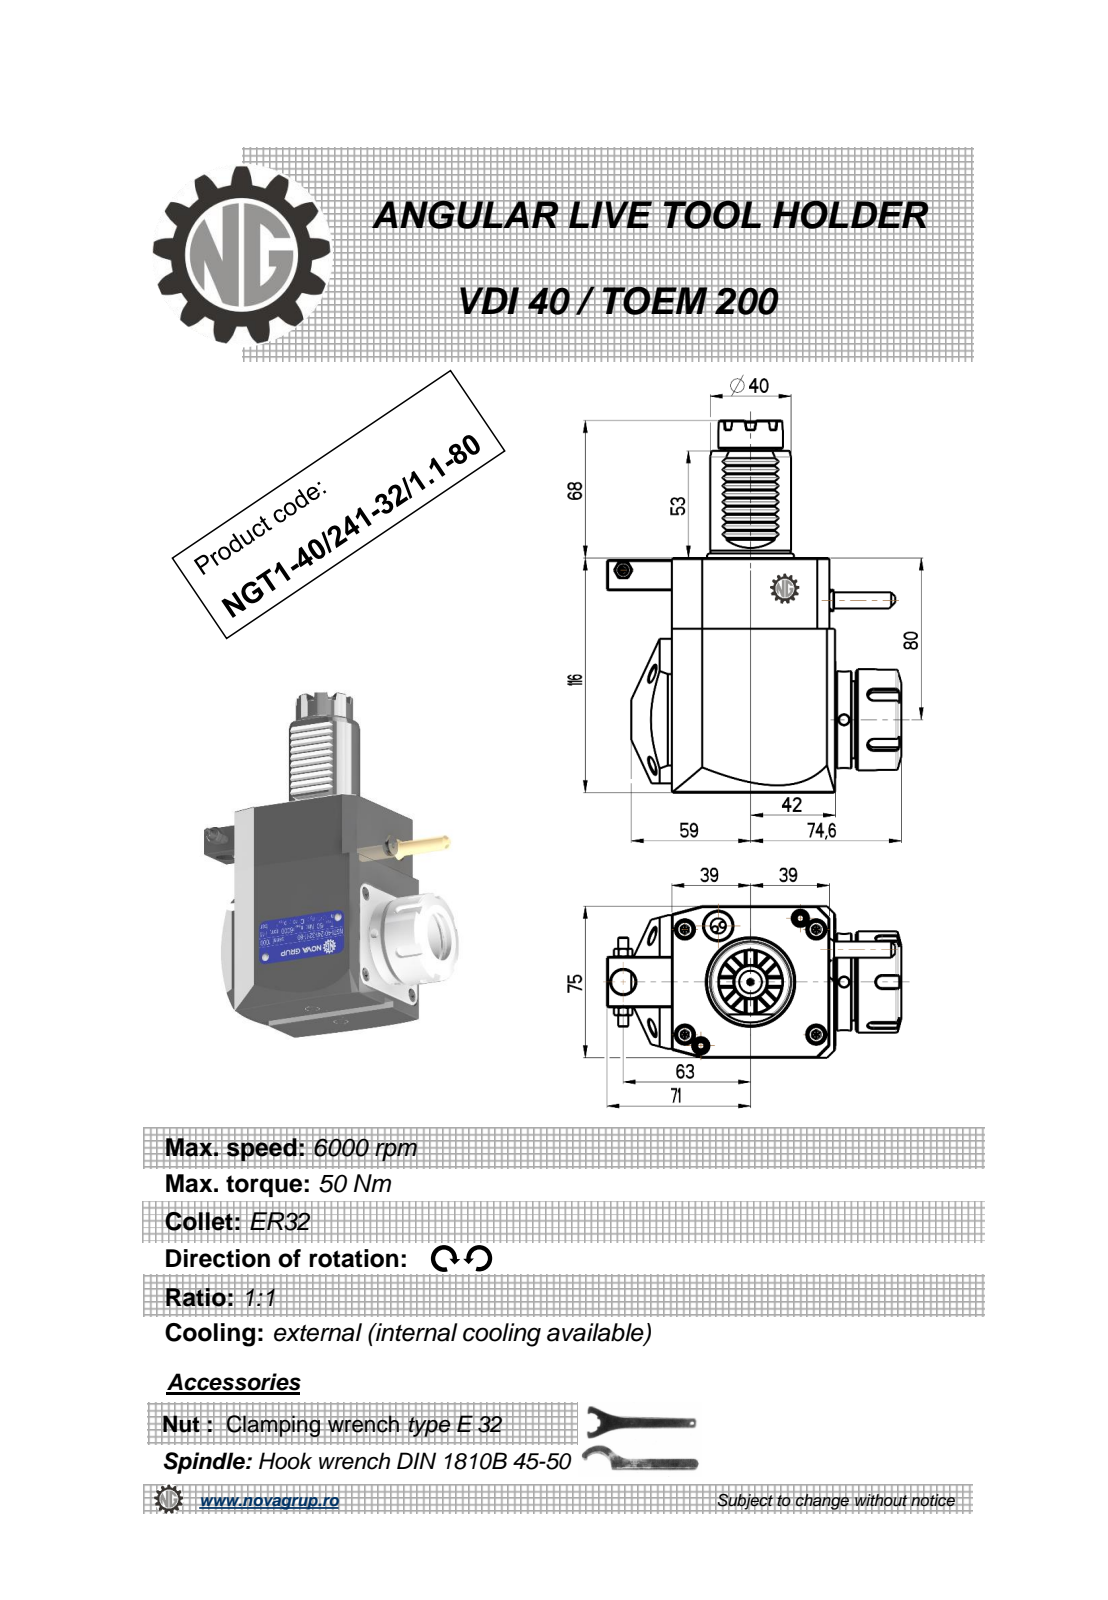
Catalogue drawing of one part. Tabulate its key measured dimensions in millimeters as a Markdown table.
| quantity | value |
| --- | --- |
| part name | NGT1_40_241_32_1_1_80 |
| STEP written by | PRO/ENGINEER BY PARAMETRIC TECHNOLOGY CORPORATION, 2010280 (CONFIG_CONTROL_DESIGN) |
| units | millimeters |
| bodies | 1 solid, 491 faces (227 planar, 97 cylindrical, 167 other) |
| overall size | 184 × 145.6 × 76.6 |
| volume | 877 556 mm³ |
| surface area | 71 446 mm² |
| round holes (diameter × count) | 5 × 3, 3 × 1, 4.2 × 1, 9.5 × 1, 12 × 1, 27 × 1 |
| round bosses / shafts (diameter × count) | 50 × 1, 48 × 1, 41 × 1, 40 × 1, 32 × 1, 17 × 1, 11.2 × 1, 8.96 × 1 |
| partial cylindrical surfaces (radius × count) | 0.26 × 12, 0.3 × 10, 0.22 × 6, 3 × 5, 0.5 × 1, 8.6 × 1, 40 × 1 |
| main face-to-face distances | 75, 116, 81, 78, 3, 80.8, 2.8, 25, 4.5, 1 |
| hole center spacings | 20.93, 61.13, 72.5, 109.25, 131.95 |
